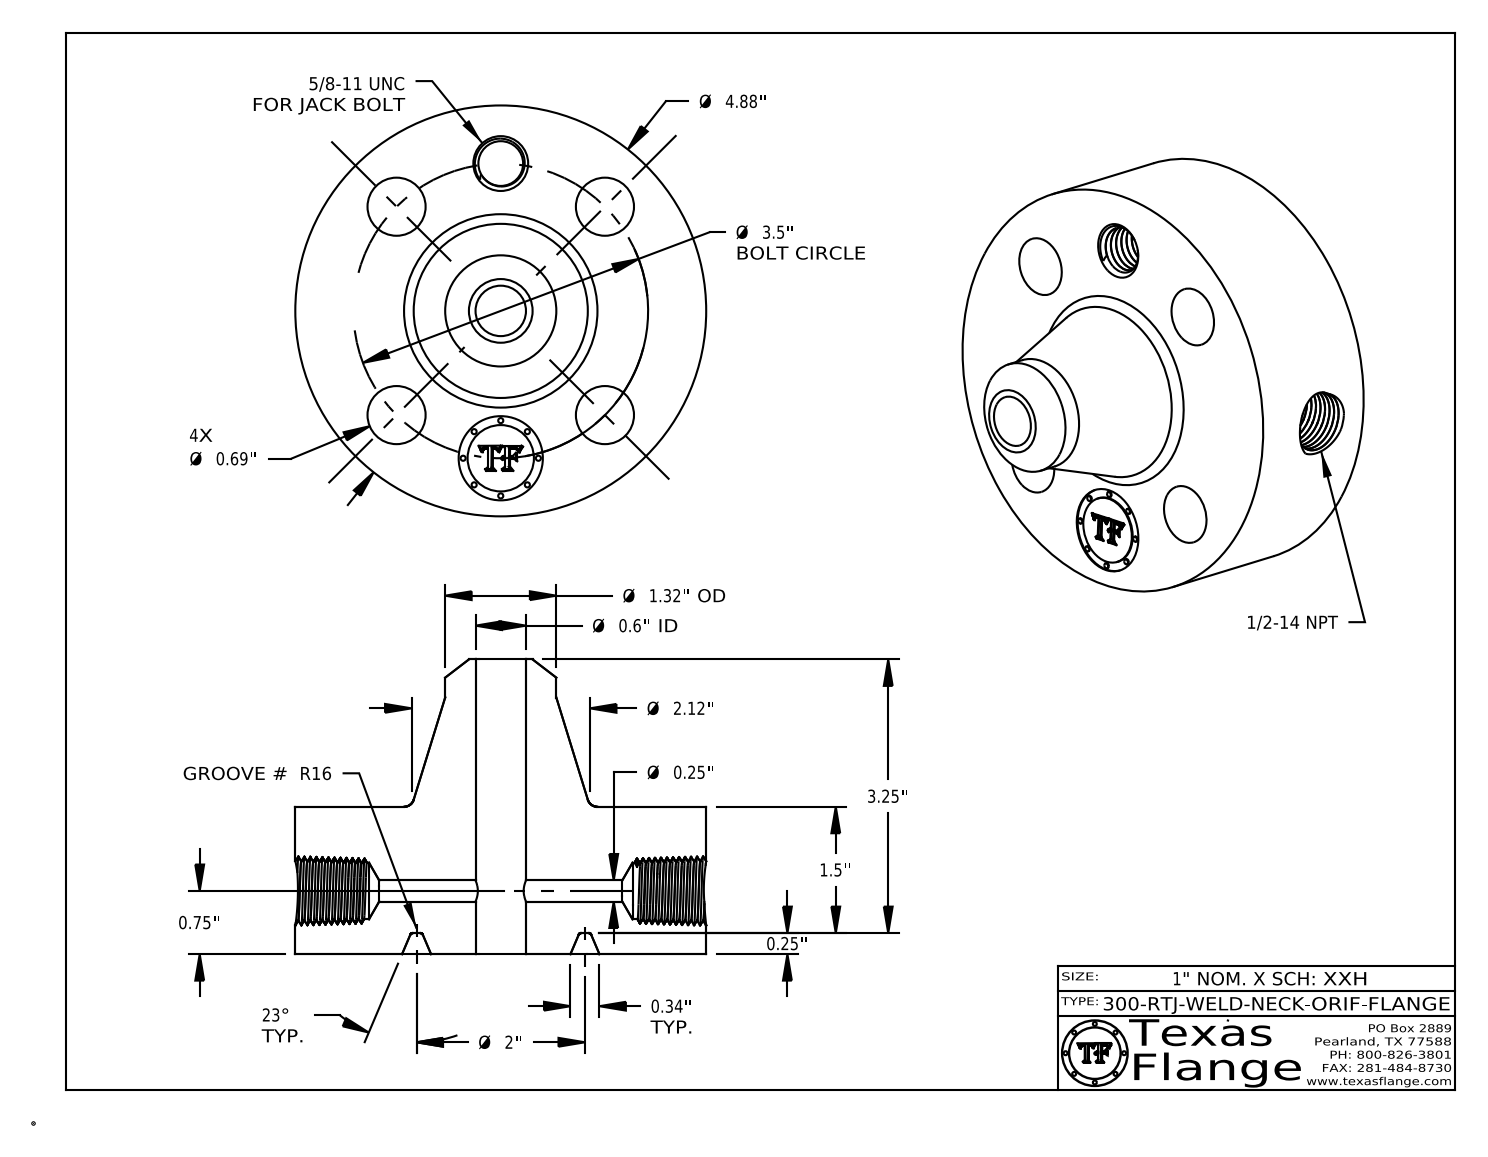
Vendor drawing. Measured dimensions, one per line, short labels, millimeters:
name: 300-RTJ-WELD-NECK
written by: CATIA V5 STEP AP214 (AUTOMOTIVE_DESIGN)
unit: mm
bodies: 1 solid, 789 faces (370 planar, 91 cylindrical, 328 other)
size: 124 × 124 × 88.9
volume: 507 800 mm³; area: 66 770 mm²
holes: 4× ⌀17.5, 1× ⌀6.4, 1× ⌀13.5, 1× ⌀15.2, 1× ⌀17.1, 1× ⌀25.4
bosses: 8× ⌀1.5, 1× ⌀124, 1× ⌀33.5, 1× ⌀20
face distances: 44.5, 6.4, 38.1, 44.1, 37.7, 0.4, 88.9, 82.6, 44.8, 7.6
hole spacings: 44.5, 34, 62.9, 82.1, 88.9
